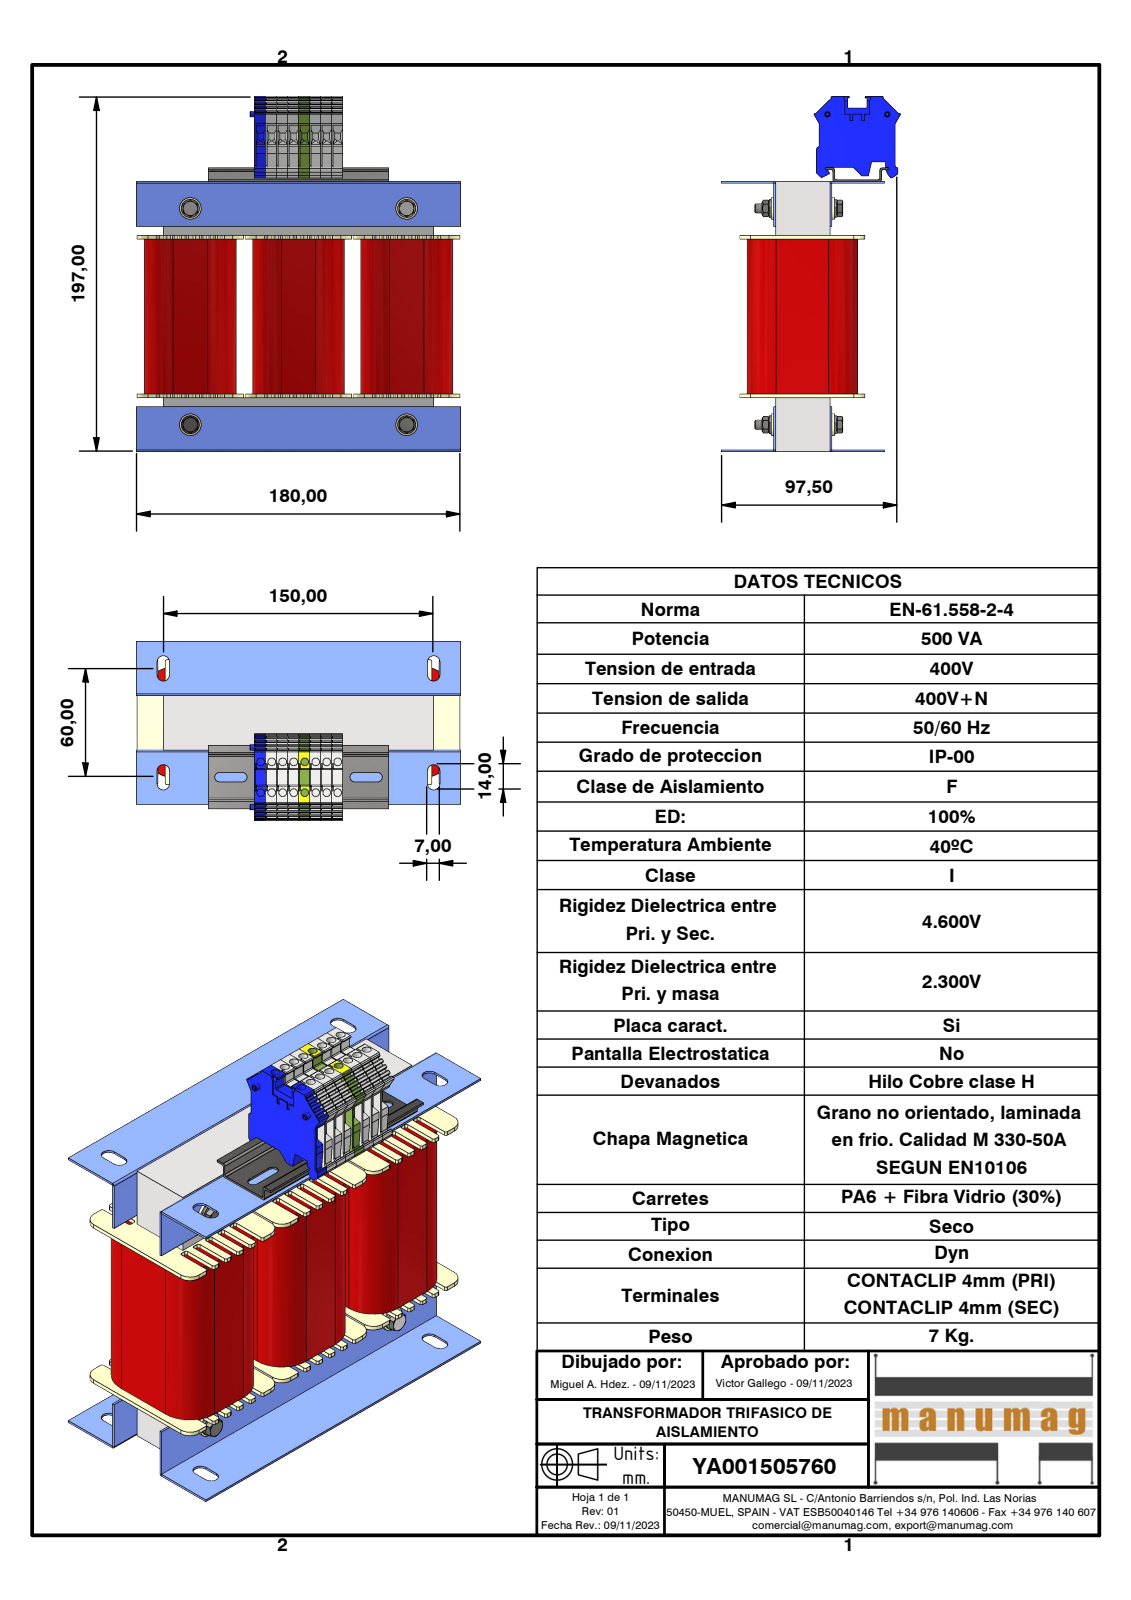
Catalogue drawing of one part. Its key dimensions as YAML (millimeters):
part_name: "YA001505760; 3UI90 150 x 150 - 30 (Rc30); UI 90_30; RC30 NT030 (+8 more)"
step_written_by: "Autodesk Inventor 2023 (AUTOMOTIVE_DESIGN)"
units: millimeters
bodies: {solids: 41, faces: 3082, planar: 2178, cylindrical: 736, other: 168}
overall_size: [197.25, 180, 99.03]
volume: 1166000
surface_area: 321694
round_holes:
  - {diameter: 4.3, count: 16}
  - {diameter: 4.13, count: 4}
  - {diameter: 5, count: 4}
  - {diameter: 5.3, count: 4}
  - {diameter: 6, count: 4}
  - {diameter: 10.5, count: 4}
  - {diameter: 2.4, count: 2}
  - {diameter: 2.5, count: 2}
  - {diameter: 2.75, count: 2}
  - {diameter: 2.95, count: 2}
round_bosses_or_shafts:
  - {diameter: 12, count: 4}
  - {diameter: 10, count: 4}
  - {diameter: 6.7, count: 4}
  - {diameter: 5.9, count: 4}
  - {diameter: 4.57, count: 4}
partial_cylinders:
  - {radius: 1, count: 132}
  - {radius: 0.25, count: 16}
  - {radius: 6, count: 12}
  - {radius: 16, count: 12}
  - {radius: 2.6, count: 8}
  - {radius: 3.5, count: 8}
  - {radius: 0.3, count: 5}
  - {radius: 0.5, count: 5}
face_to_face_distances: [30, 1, 120, 60, 31, 90, 150, 149, 119, 6.1]
hole_center_spacings: [6.1, 18.06, 12.2, 20.92, 18.3, 24.98, 17, 24.4]
